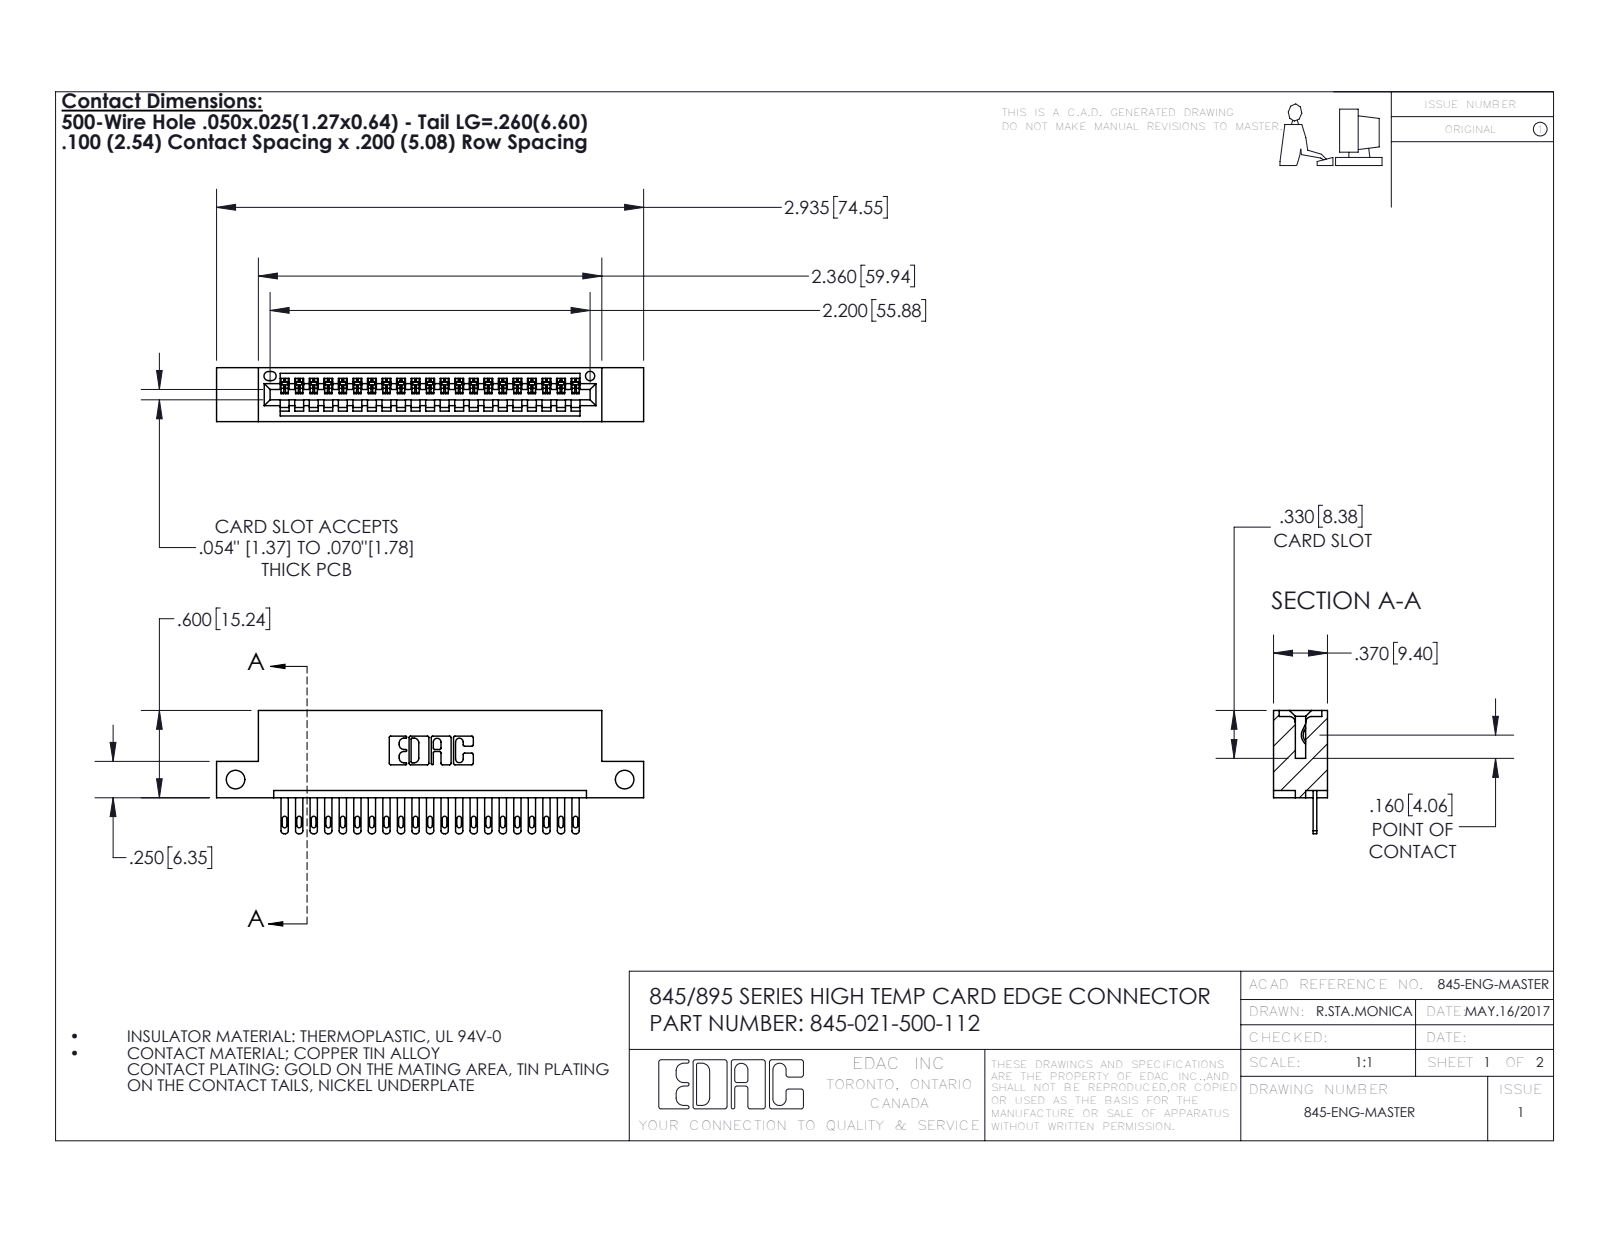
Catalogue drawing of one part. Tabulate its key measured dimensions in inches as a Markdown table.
| quantity | value |
| --- | --- |
| part name | 345 Part_Flush Mounting Lugs - Side Mount; 345-292-001_345-293-100; 345-021-500-112 |
| STEP written by | SolidWorks 2016 (CONFIG_CONTROL_DESIGN) |
| units | inches |
| bodies | 22 solids, 1260 faces (794 planar, 466 cylindrical, 0 other) |
| overall size | 2.935 × 0.847 × 0.37 |
| volume | 0.417 in³ |
| surface area | 13.49 in² |
| round holes (diameter × count) | 0.128 × 2, 0.064 × 1 |
| partial cylindrical surfaces (radius × count) | 0.006 × 42, 0.016 × 42, 0.02 × 42, 0.01 × 22, 0.007 × 6, 0.031 × 6, 0.026 × 3, 0.031 × 2 |
| main face-to-face distances | 0.298, 0.072, 0.2, 0.37, 0.098, 0.272, 0.025, 0.225, 0.149, 0.05 |
| hole center spacings | 2.675 |
